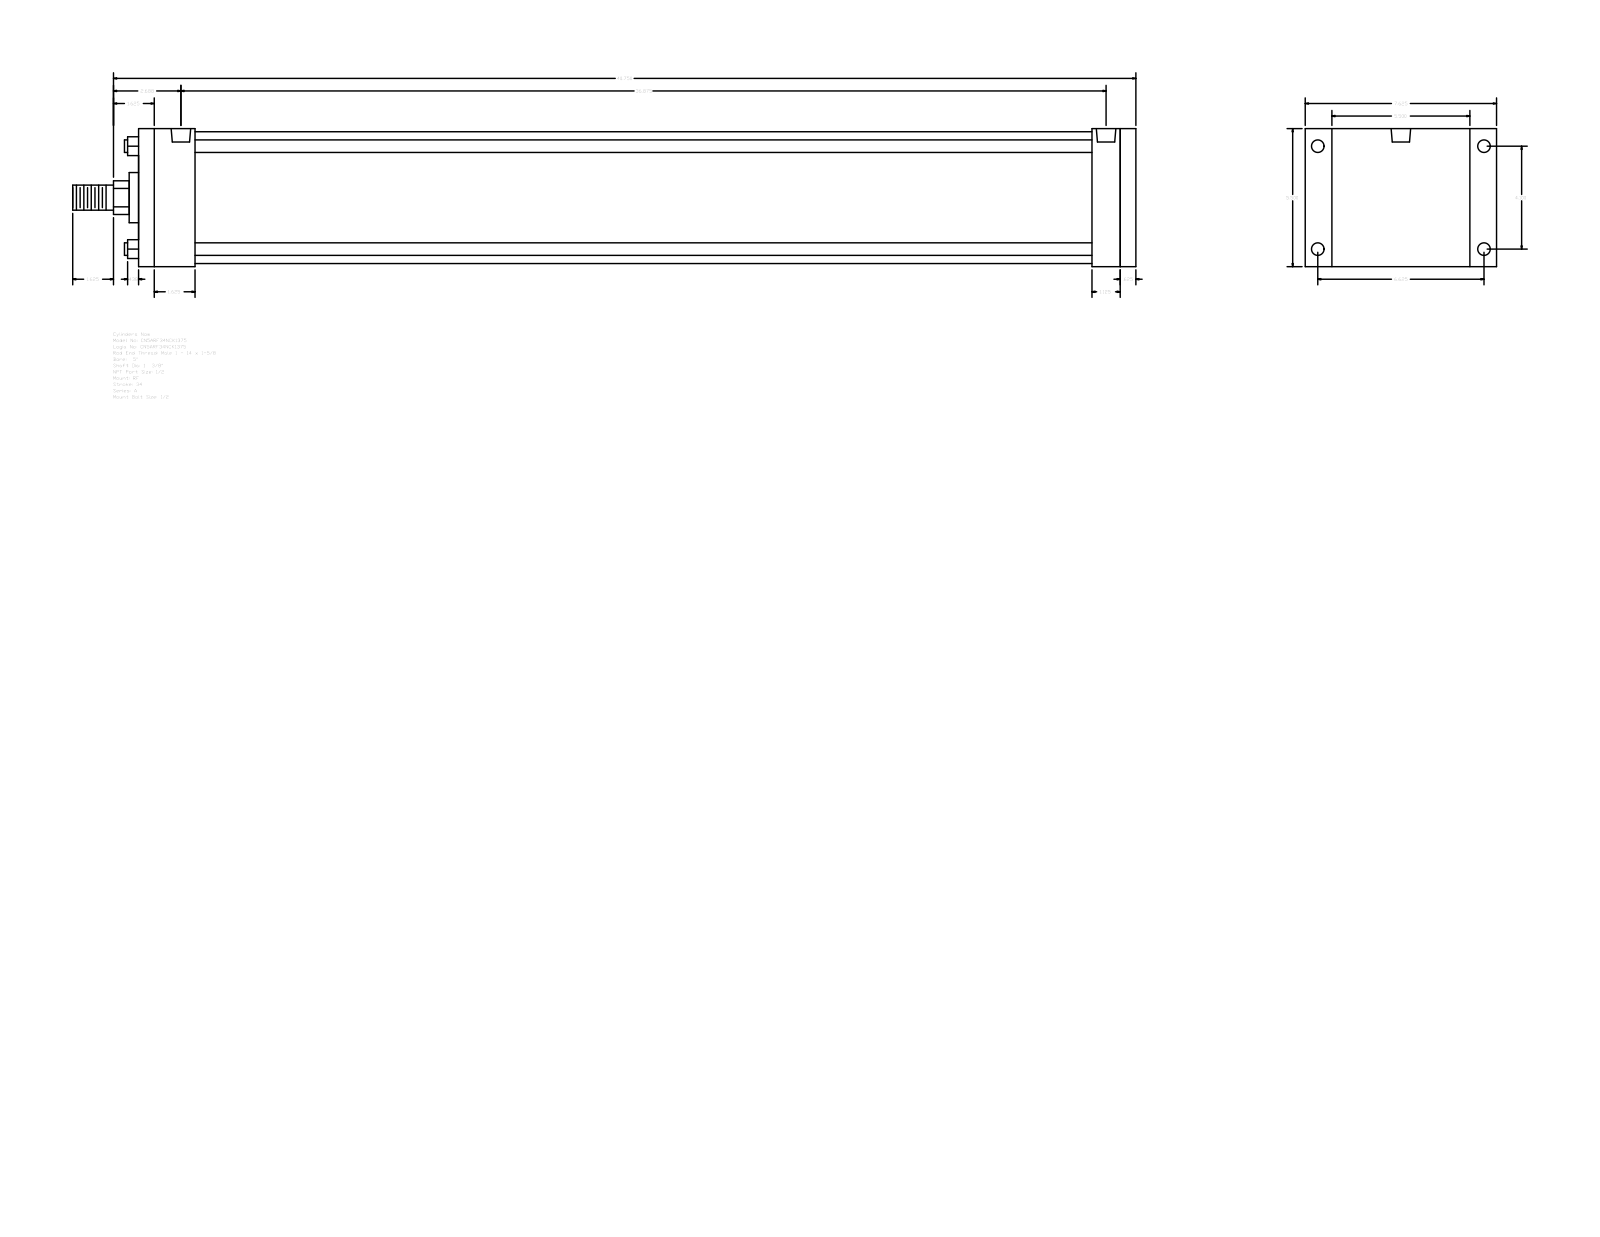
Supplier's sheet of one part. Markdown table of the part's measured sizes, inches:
| quantity | value |
| --- | --- |
| part name | A_RF__0500_1.375 |
| STEP written by | GSSL Pune (CONFIG_CONTROL_DESIGN) |
| units | inches |
| bodies | 0 solids, 92 faces (64 planar, 28 cylindrical, 0 other) |
| overall size | 42.375 × 7.625 × 5.5 |
| round holes (diameter × count) | 0.344 × 4, 0.5 × 4, 0.778 × 2 |
| round bosses / shafts (diameter × count) | 0.5 × 4, 5.25 × 1, 2 × 1, 1.375 × 1, 1 × 1 |
| partial cylindrical surfaces (radius × count) | 0.672 × 1 |
| main face-to-face distances | 5.5, 39.75, 0.625, 39.125, 2.25, 36.875, 37.5, 38, 35.75, 1.125 |
| hole center spacings | 0.094, 4.1, 6.625, 7.791, 36.687, 36.781, 36.875 |
